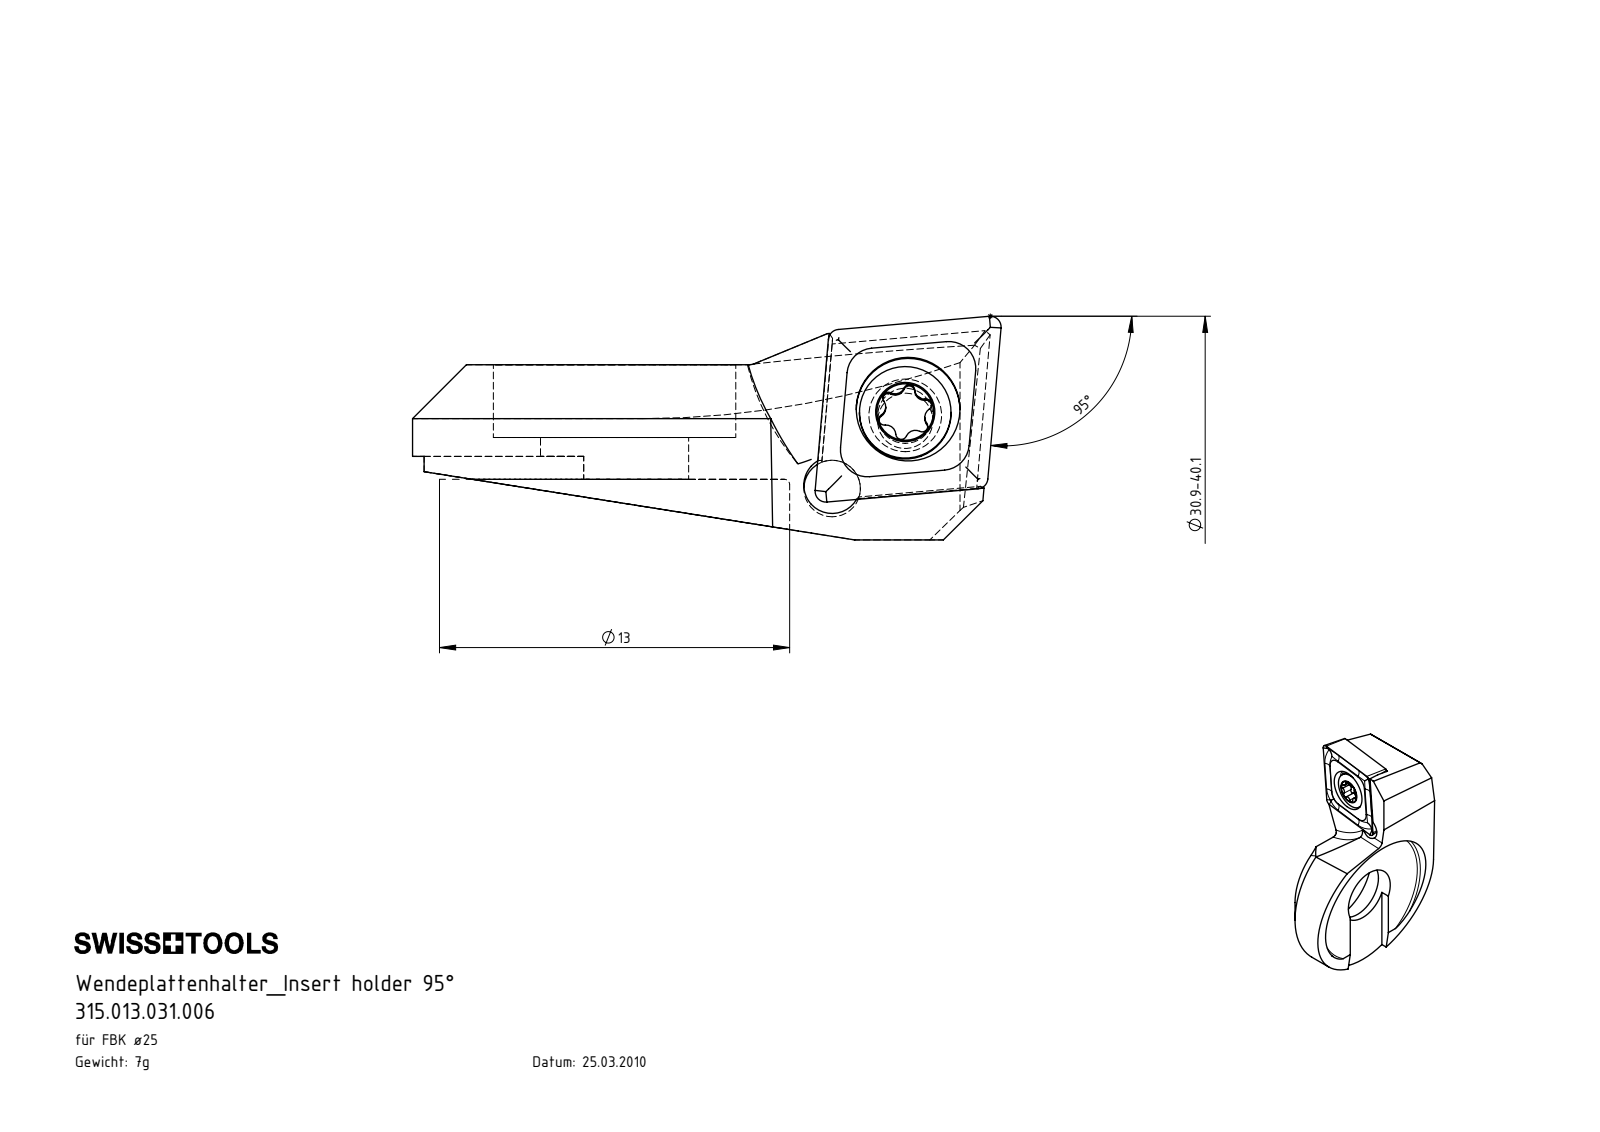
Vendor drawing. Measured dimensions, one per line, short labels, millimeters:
name: WCA-ER2.001.006_A; CCMT060204; 315.013.031.006; F25-WCA.002.006_C_fertigbearbeitet
written by: SolidWorks 2017 (CONFIG_CONTROL_DESIGN)
unit: mm
bodies: 5 solids, 143 faces (49 planar, 43 cylindrical, 51 other)
size: 21.85 × 15 × 8.3
volume: 875 mm³; area: 1 309 mm²
holes: 1× ⌀2.05, 1× ⌀2.1, 1× ⌀2.8, 1× ⌀3.85, 1× ⌀5.5, 1× ⌀9
bosses: 1× ⌀3.4, 1× ⌀2.5
rounds: 6× R0.21, 5× R0.36, 2× R0.5, 1× R0.36, 1× R1.05, 1× R6.5, 1× R7.5, 1× R9
face distances: 4.25, 4.15, 2.27, 2.7, 2.6, 1.55, 2.28, 3.4, 3.3, 0.7
hole spacings: 3.84, 3.99
